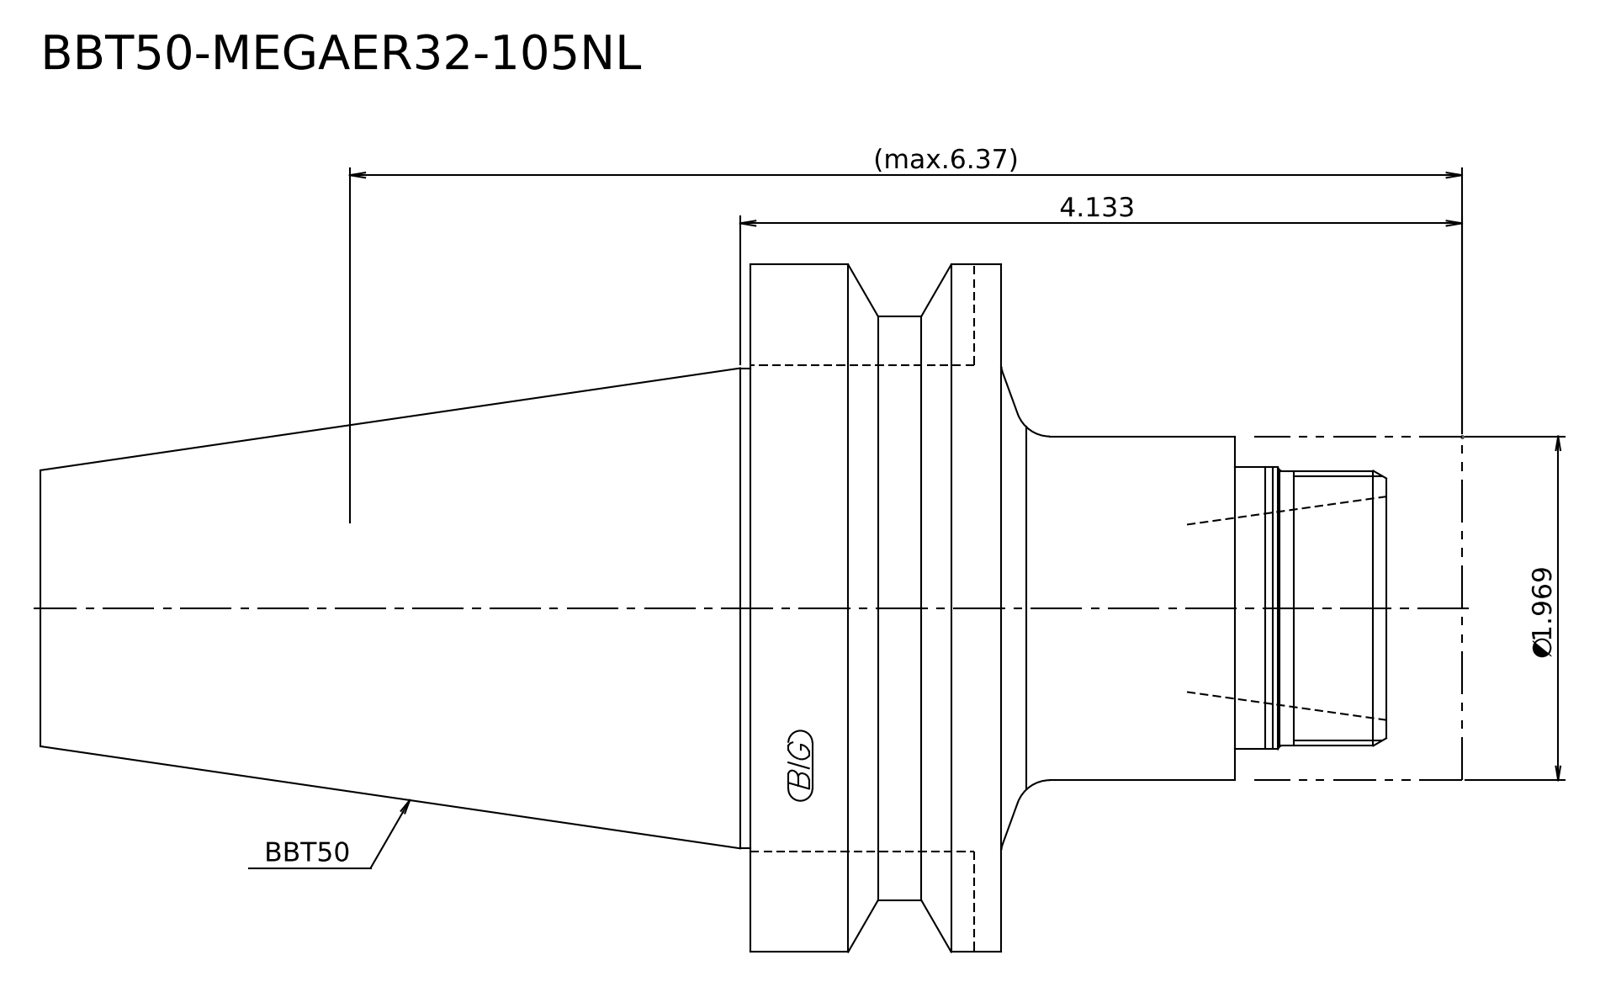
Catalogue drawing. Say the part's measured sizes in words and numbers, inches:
Its 3-D file was written by "Kubotek KeyCreator 2011 V10.0.2 (22737) (automotive_design)". It is 2 solids with 21 faces: 7 planar, 8 cylindrical and 6 other. Overall it measures 206.8 by 100 by 100 inches. Its volume is 677 045 cubic inches and its surface area 60 703 square inches. Round bosses or shafts: 1 of diameter 100, 1 of diameter 85, 1 of diameter 69.85, 1 of diameter 50, 1 of diameter 41, 1 of diameter 40. The main face-to-face distances are 36.5, 36.8, 73.3, 30.2, 67, 103.5, 206.8, 176.6, 139.8, 103.3.
